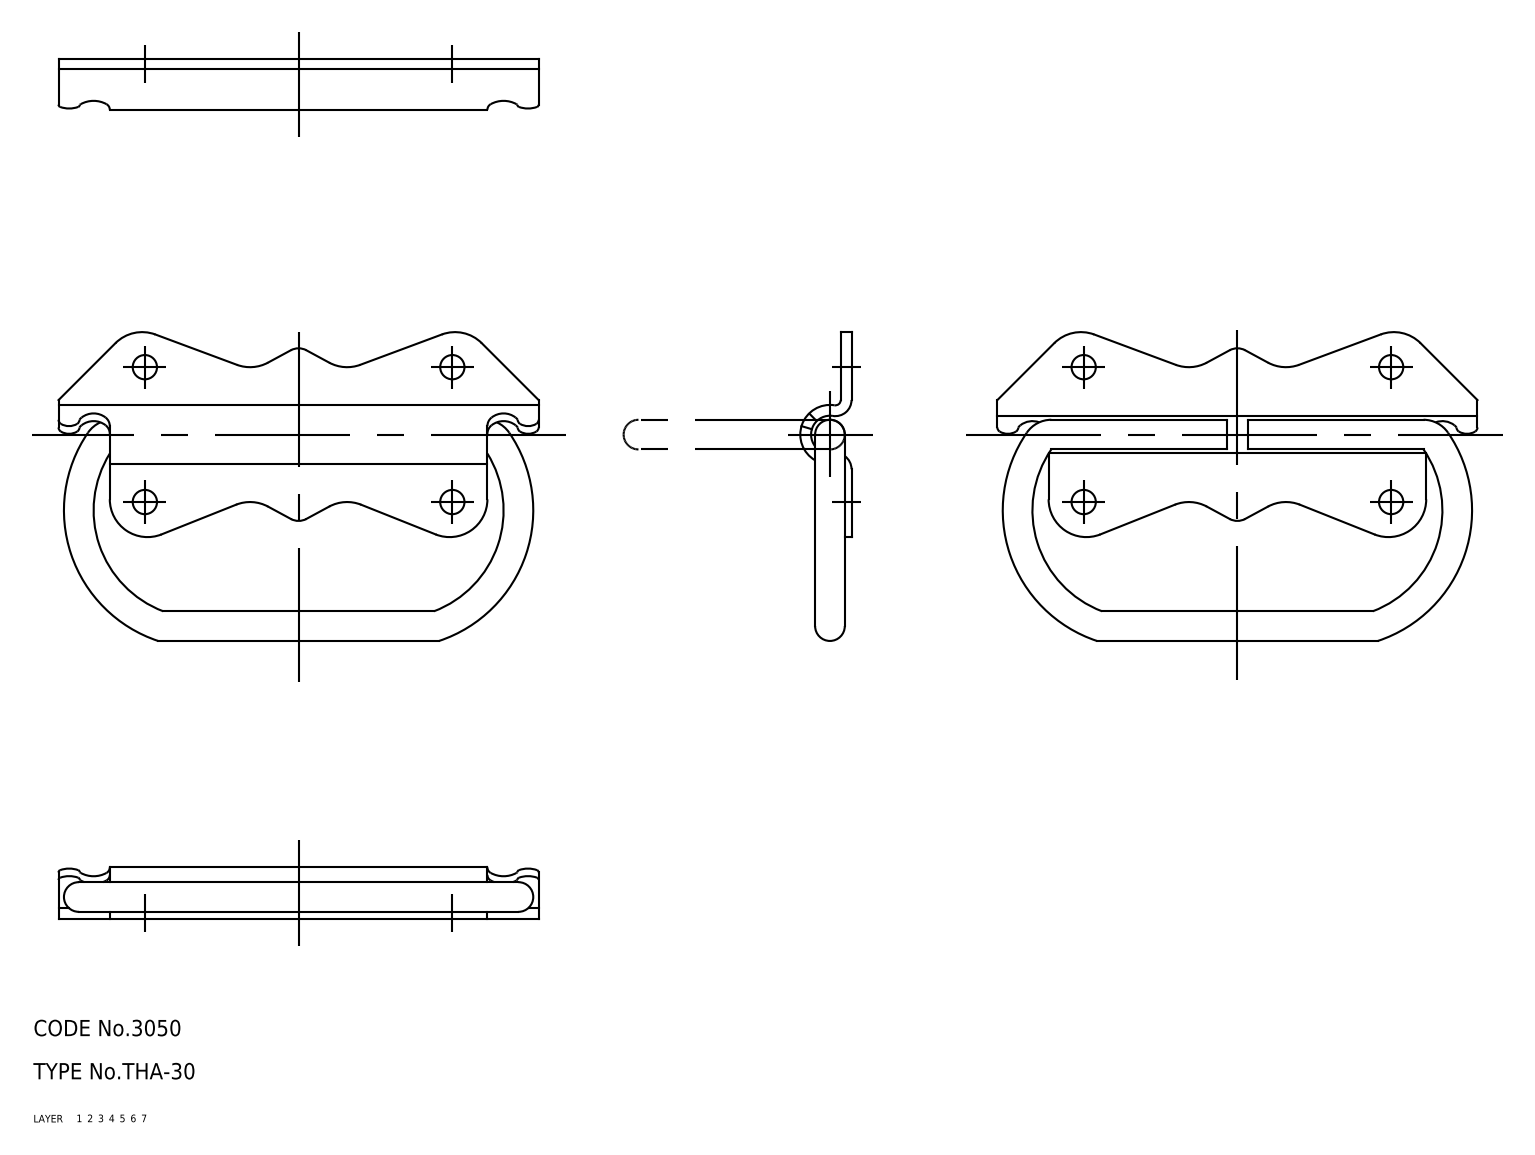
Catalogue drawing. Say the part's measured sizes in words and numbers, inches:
The part is named "grip; base; THA_30_14135_36". Its 3-D file was written by "CADfix (AUTOMOTIVE_DESIGN)". It is 2 solids with 78 faces: 0 planar, 0 cylindrical and 78 other. Overall it measures 3.504 by 2.254 by 0.374 inches. Its volume is 0.668 cubic inches and its surface area 15.98 square inches.
